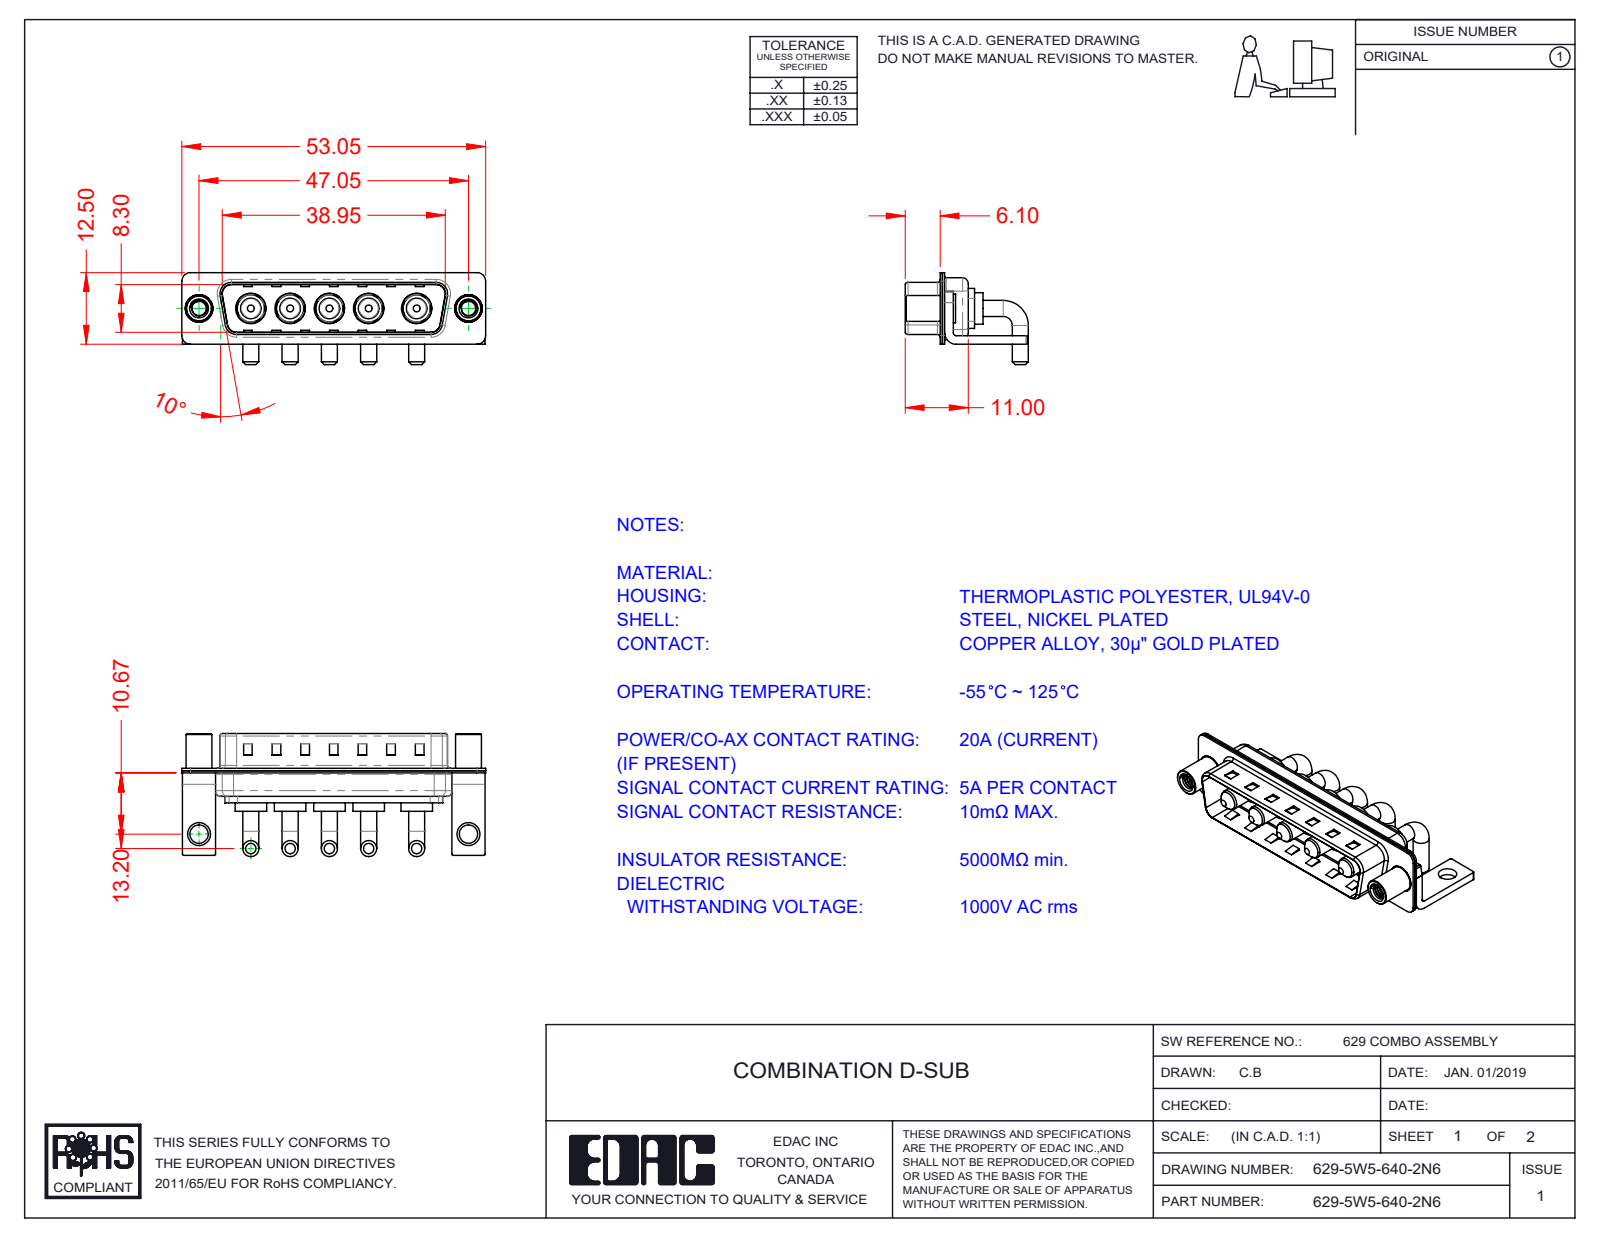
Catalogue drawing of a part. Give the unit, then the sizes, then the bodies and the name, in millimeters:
Units: millimetres
Overall size (bounding box): 53.05 × 21.5 × 16.05
Round holes (diameter × count): ⌀4.85 ×5, ⌀5.3 ×5, ⌀2.5 ×2, ⌀3.2 ×2, ⌀4 ×2, ⌀4.8 ×2
Round bosses / shafts (diameter × count): ⌀2.8 ×10, ⌀5.5 ×5, ⌀5.2 ×5, ⌀4.75 ×5, ⌀3.75 ×5, ⌀3.6 ×5, ⌀5 ×2, ⌀4.9 ×2
Partial cylindrical surfaces — rounded edges, fillets, slot ends (radius × count): R0.25 ×16, R1.5 ×16, R2 ×13, R0.5 ×9, R1.6 ×8, R2.1 ×5, R0.6 ×4, R0.65 ×4
Main face-to-face distances: 0.4, 0.8, 9.5, 1.5, 9.1, 8.7, 9.9, 5.2, 0.75, 1.2
Hole centre spacings: 6.86, 13.73, 47.05, 6.85, 6.87, 8.37, 8.38, 9.04
Volume: 3 785 mm³ · Surface area: 8 071 mm²
Bodies: 17 solids, 689 faces (243 planar, 314 cylindrical, 132 other)
Part name (STEP PRODUCT): 629Combo Shell Front_25 Contacts; 629Combo Stabilizer Bracket; 629-5W5-640-2N6; 629Combo Housing_5W5 (+3 more)
STEP written by: SolidWorks 2020 (CONFIG_CONTROL_DESIGN)
